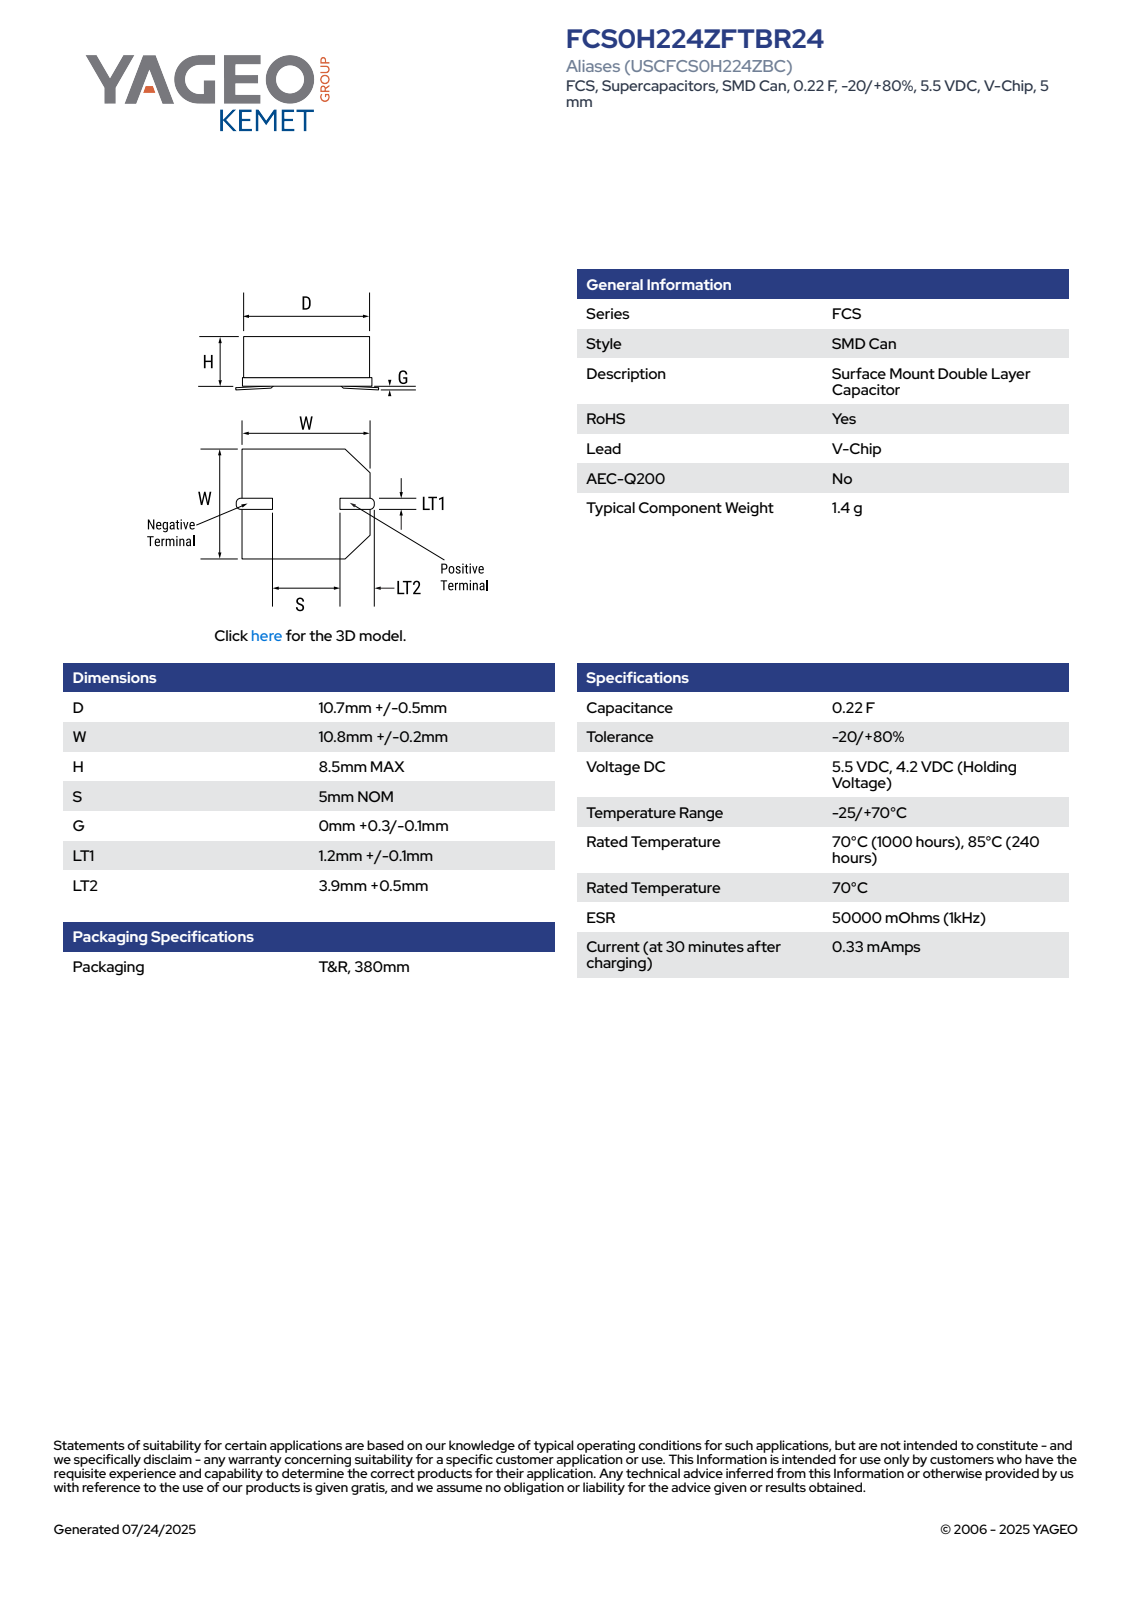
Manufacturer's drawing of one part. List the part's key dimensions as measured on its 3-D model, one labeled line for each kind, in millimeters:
Part name (STEP PRODUCT): CDC_VC_D10.7L8.5LT11.3G0.3W11LT24.4
STEP written by: SolidWorks 2014 (AUTOMOTIVE_DESIGN)
Units: millimetres
Bodies: 5 solids, 60 faces (49 planar, 5 cylindrical, 6 other)
Overall size (bounding box): 13.8 × 11 × 8.51
Volume: 787 mm³ · Surface area: 729 mm²
Round bosses / shafts (diameter × count): ⌀10.7 ×1
Partial cylindrical surfaces — rounded edges, fillets, slot ends (radius × count): R0.2 ×2, R4.25 ×1
Main face-to-face distances: 2.12, 8.2, 6.08, 11, 2.42, 8.5, 4.85, 6.15, 1.3, 1.4
